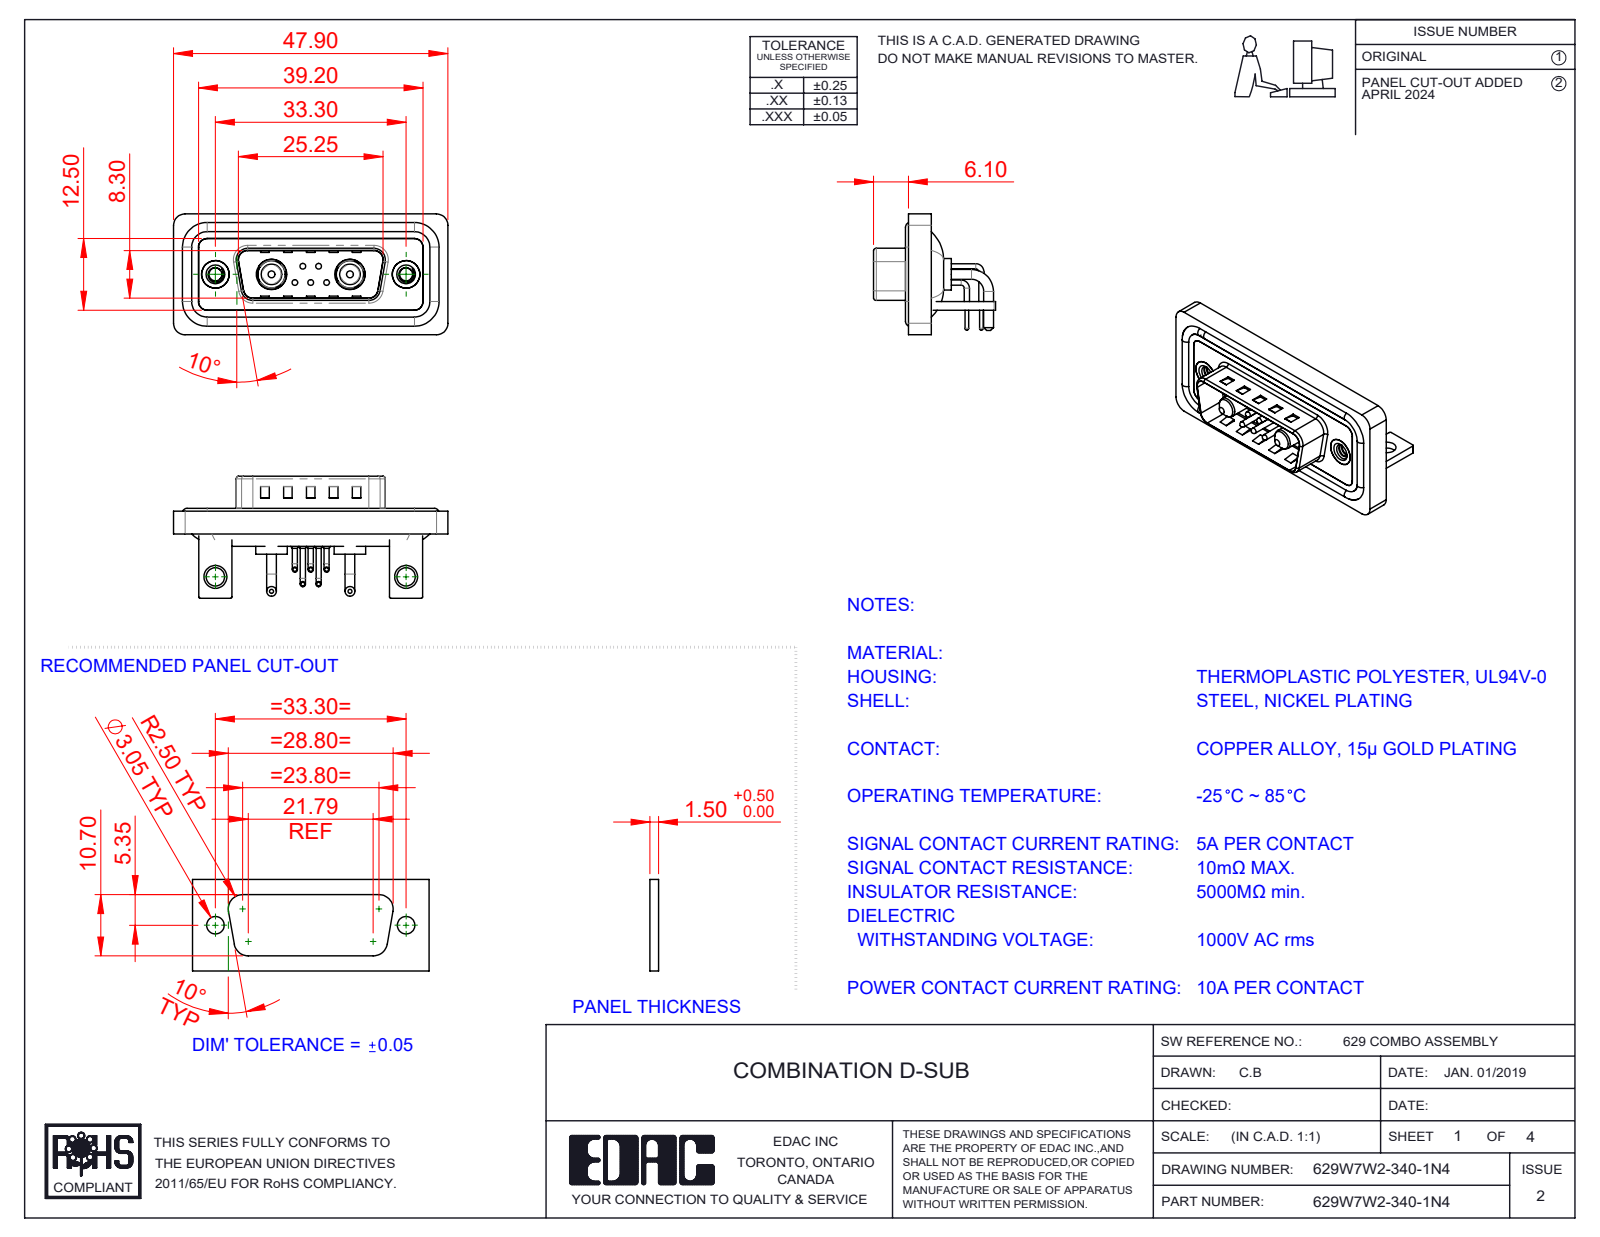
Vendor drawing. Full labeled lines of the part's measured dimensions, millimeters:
Part name (STEP PRODUCT): 629Combo Contact Row 2; 629Combo Waterproof Housing_15 Contacts; 629Combo Shell Front_15 Contacts; 629Combo Shell Rear_15 Contacts (+6 more)
STEP written by: SolidWorks 2023 (CONFIG_CONTROL_DESIGN)
Units: millimetres
Bodies: 18 solids, 1123 faces (537 planar, 424 cylindrical, 162 other)
Overall size (bounding box): 47.9 × 21.3 × 21.1
Volume: 5 842 mm³ · Surface area: 9 626 mm²
Round holes (diameter × count): ⌀0.75 ×5, ⌀1.6 ×5, ⌀2 ×5, ⌀2.26 ×2, ⌀3.2 ×2, ⌀4 ×2, ⌀4.8 ×2, ⌀4.85 ×2, ⌀5 ×2, ⌀5.3 ×2
Round bosses / shafts (diameter × count): ⌀0.9 ×10, ⌀1.5 ×5, ⌀1 ×5, ⌀0.65 ×5, ⌀1.7 ×4, ⌀1.6 ×4, ⌀5.5 ×2, ⌀5.2 ×2
Partial cylindrical surfaces — rounded edges, fillets, slot ends (radius × count): R2 ×21, R1.5 ×18, R0.25 ×16, R0.5 ×9, R1.6 ×8, R1.01 ×5, R0.6 ×4, R0.65 ×4
Main face-to-face distances: 0.4, 1.5, 0.8, 2.9, 2.1, 1.1, 1.6, 1.2, 3.7, 4.5
Hole centre spacings: 3.16, 2.77, 9.8, 23.5, 33.3, 4.31, 4.33, 5.03
